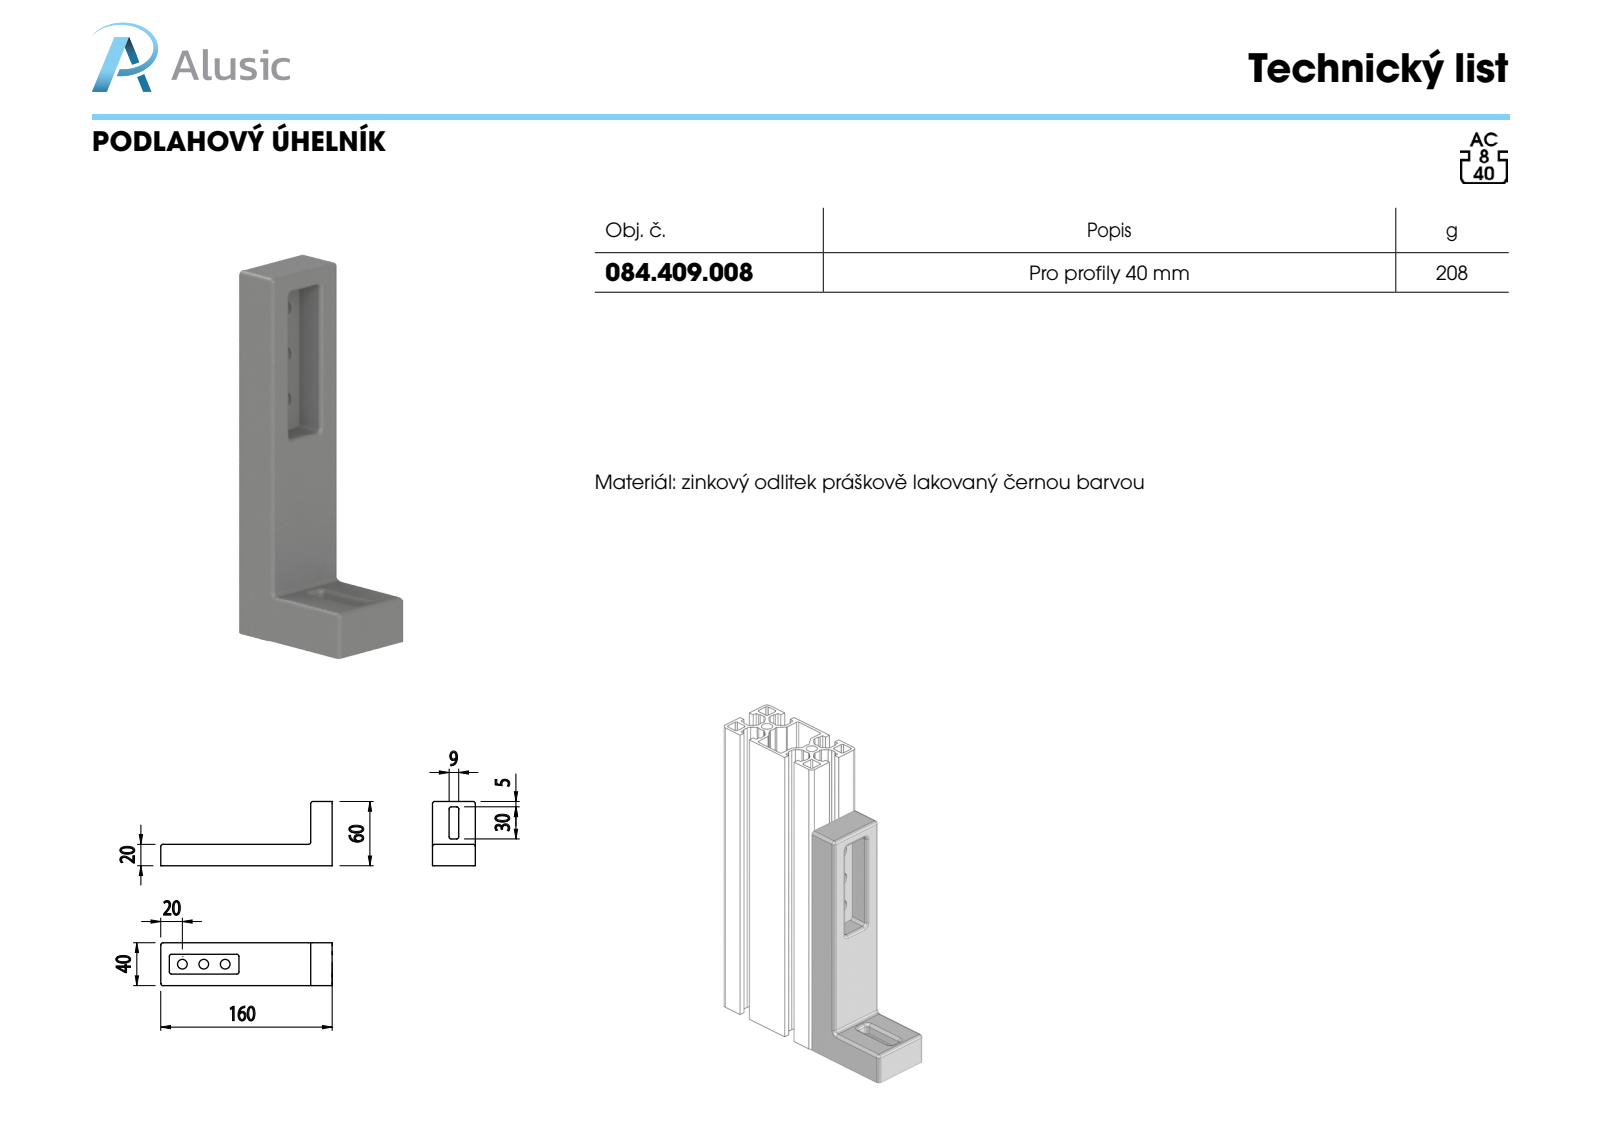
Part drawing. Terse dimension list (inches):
name: 084.409.008
written by: SolidWorks 2012 (CONFIG_CONTROL_DESIGN)
unit: in
bodies: 1 solid, 82 faces (35 planar, 33 cylindrical, 14 other)
size: 6.299 × 2.362 × 1.575
volume: 5.214 in³; area: 63.43 in²
holes: 3× ⌀0.354
rounds: 27× R0.079
face distances: 0.118, 0.315, 1.142, 1.457, 0.197, 1.26, 0.276, 0.512, 1.575, 0.787
hole spacings: 0.787, 1.575
